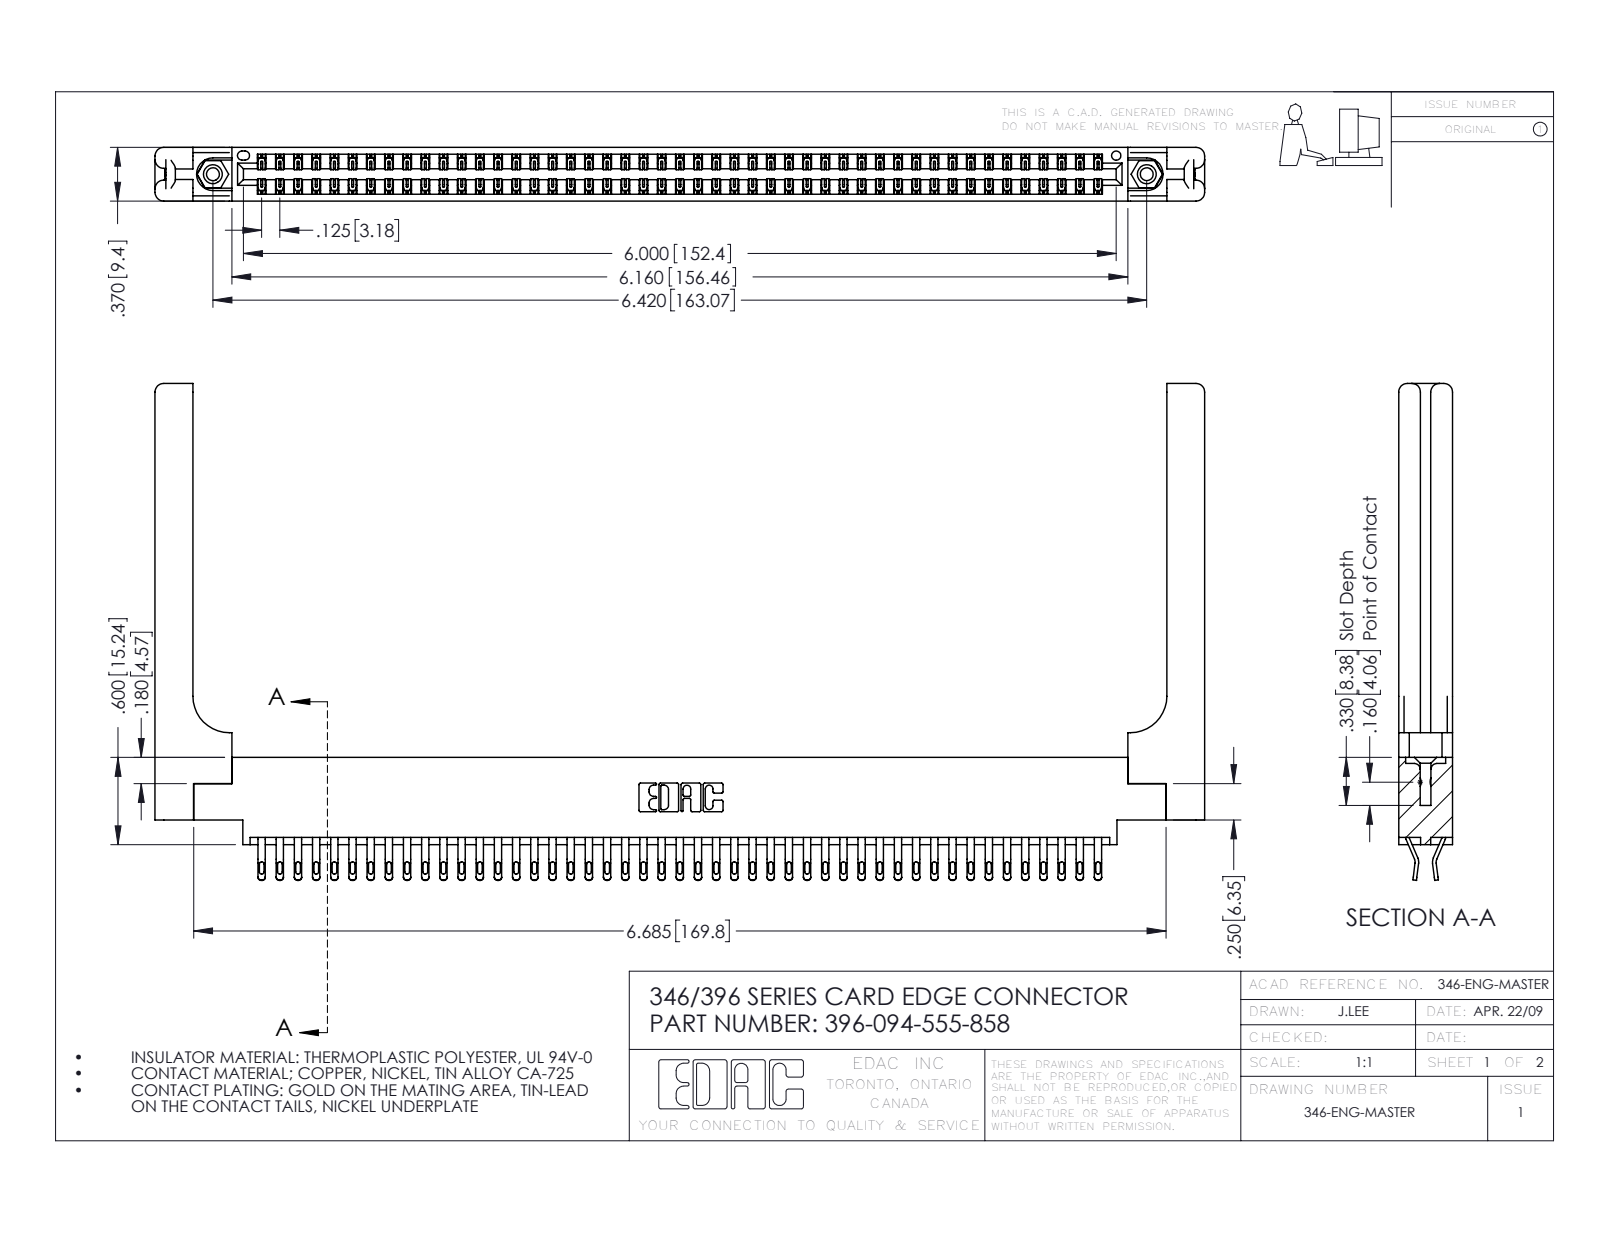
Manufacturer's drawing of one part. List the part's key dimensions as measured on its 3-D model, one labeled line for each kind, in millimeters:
Part name (STEP PRODUCT): 346-220-058_345-220-058; 346 Part_0.170 Offset - 0.156 Dia-TH; 345-250-001_345-250-001-102; 345-292-001_555 Tail (+1 more)
STEP written by: SolidWorks 2016 (CONFIG_CONTROL_DESIGN)
Units: millimetres
Bodies: 99 solids, 5834 faces (3330 planar, 2444 cylindrical, 60 other)
Overall size (bounding box): 183.3 × 86.7 × 9.4
Volume: 25 530 mm³ · Surface area: 30 990 mm²
Round holes (diameter × count): ⌀2.3 ×2, ⌀3.2 ×2, ⌀4 ×2, ⌀1.6 ×1
Round bosses / shafts (diameter × count): ⌀3.9 ×2
Partial cylindrical surfaces — rounded edges, fillets, slot ends (radius × count): R0.4 ×188, R0.5 ×188, R0.2 ×141, R0.3 ×22, R1.5 ×16, R0.2 ×6, R0.8 ×6, R0.7 ×3
Main face-to-face distances: 9.4, 1.2, 8.2, 1.8, 3.8, 3.8, 6.4, 0.6, 7.6, 7
Hole centre spacings: 6.2, 157.8, 163.1
